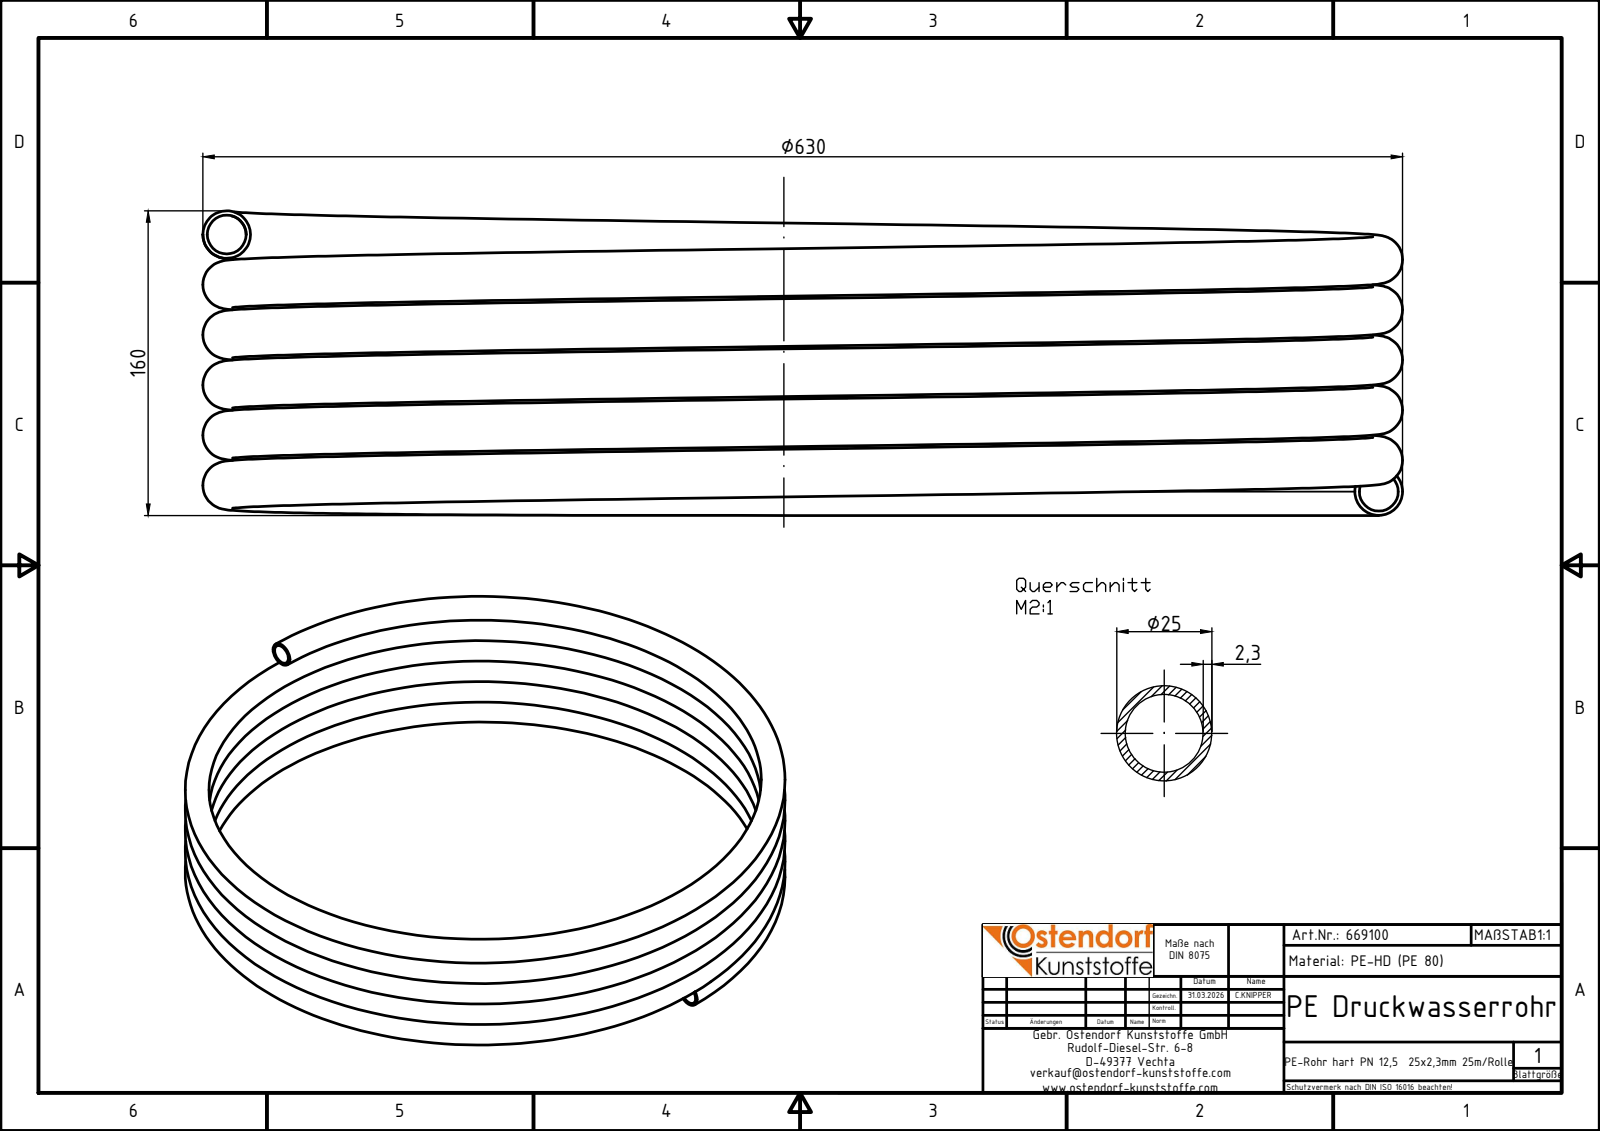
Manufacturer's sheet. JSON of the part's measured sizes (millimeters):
{"part_name": "669100z", "step_written_by": "Autodesk Inventor 2024 (AUTOMOTIVE_DESIGN)", "units": "millimeters", "bodies": {"solids": 1, "faces": 7, "planar": 3, "cylindrical": 0, "other": 4}, "overall_size": [630, 630, 159.99], "volume_mm3": 1681000, "surface_area_mm2": 1469000}
